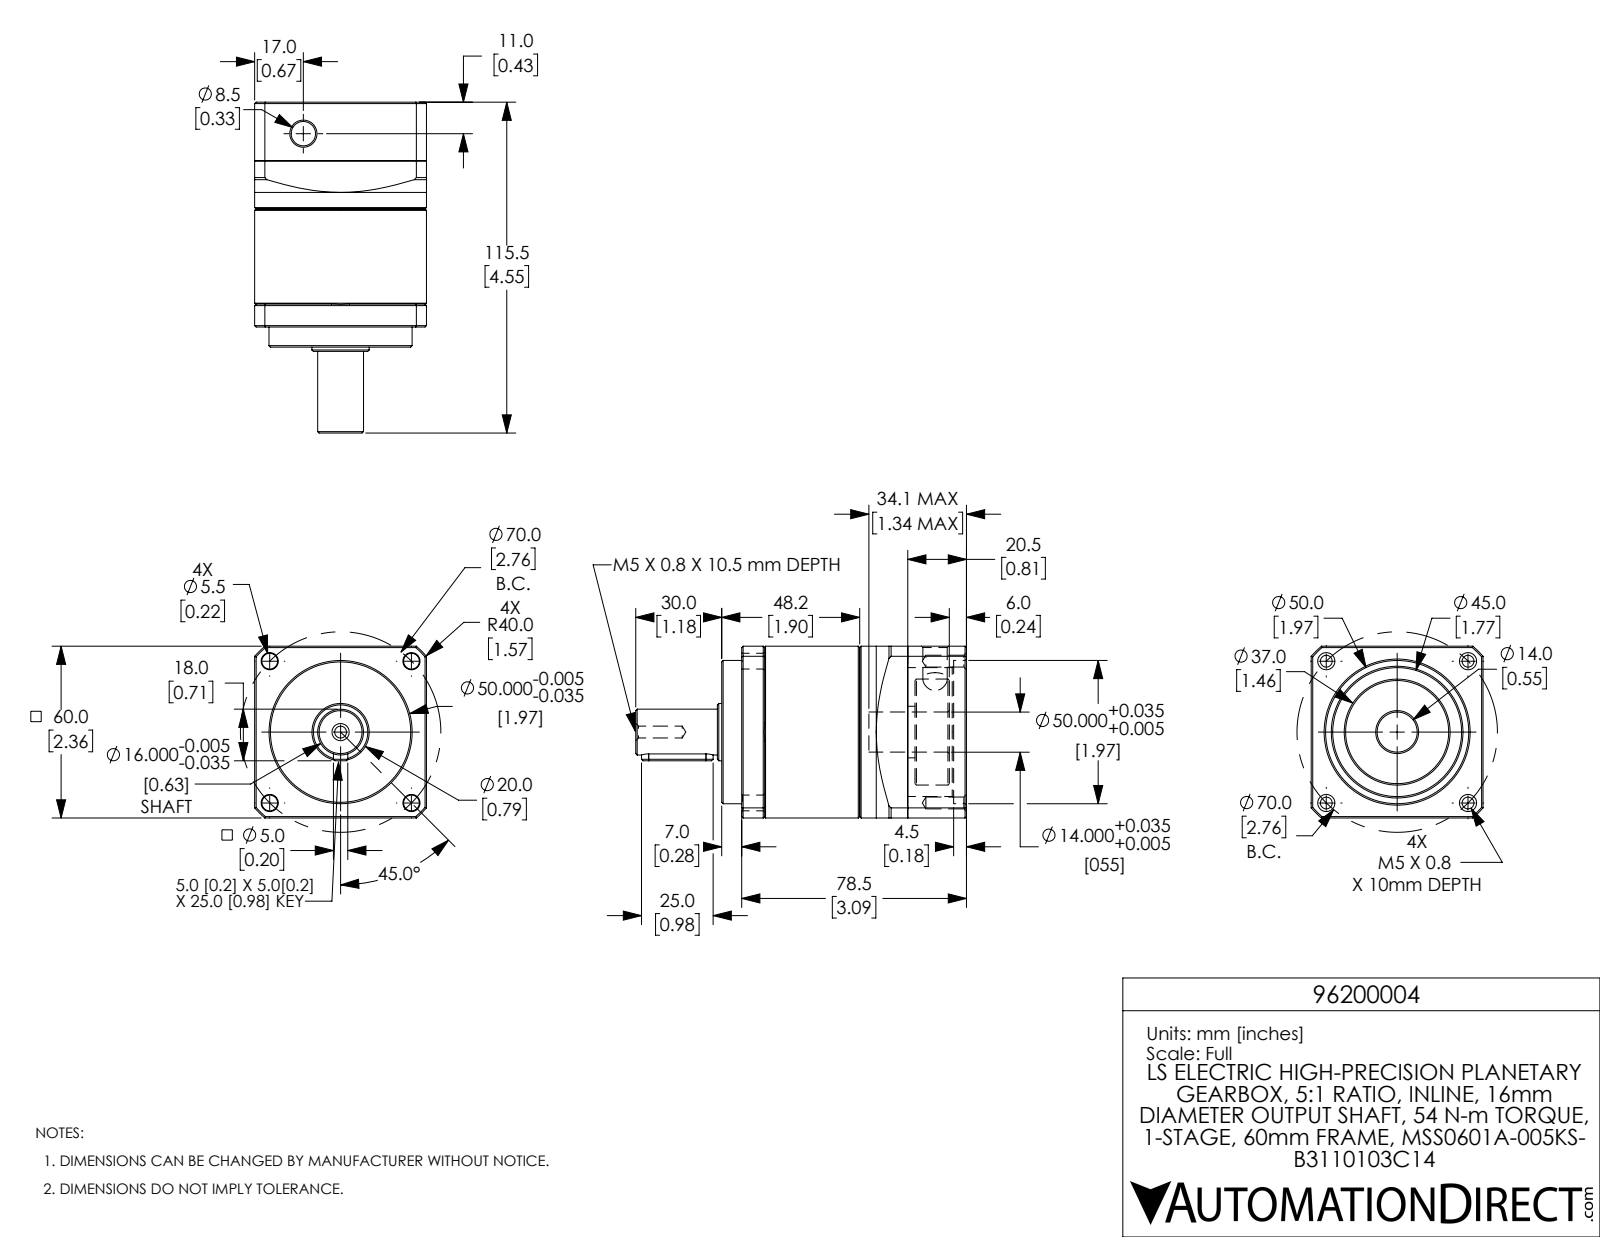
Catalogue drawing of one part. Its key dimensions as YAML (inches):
part_name: "MSS0601A-B3110103"
step_written_by: "SolidWorks 2017 (AUTOMOTIVE_DESIGN)"
units: inches
bodies: {solids: 3, faces: 183, planar: 46, cylindrical: 54, other: 83}
overall_size: [4.547, 2.362, 2.362]
volume: 14.81
surface_area: 70.54
round_holes:
  - {diameter: 0.163, count: 5}
  - {diameter: 0.217, count: 4}
  - {diameter: 0.335, count: 1}
  - {diameter: 0.551, count: 1}
  - {diameter: 1.772, count: 1}
  - {diameter: 1.969, count: 1}
round_bosses_or_shafts:
  - {diameter: 2.362, count: 1}
  - {diameter: 1.457, count: 1}
  - {diameter: 0.787, count: 1}
  - {diameter: 0.709, count: 1}
  - {diameter: 0.63, count: 1}
partial_cylinders:
  - {radius: 0.098, count: 2}
  - {radius: 1.575, count: 1}
face_to_face_distances: [0.661, 2.362, 2.559, 1.898, 2.283, 1.622, 0.276, 0.807, 1.469, 3.091]
hole_center_spacings: [1.378, 1.949, 2.756]
